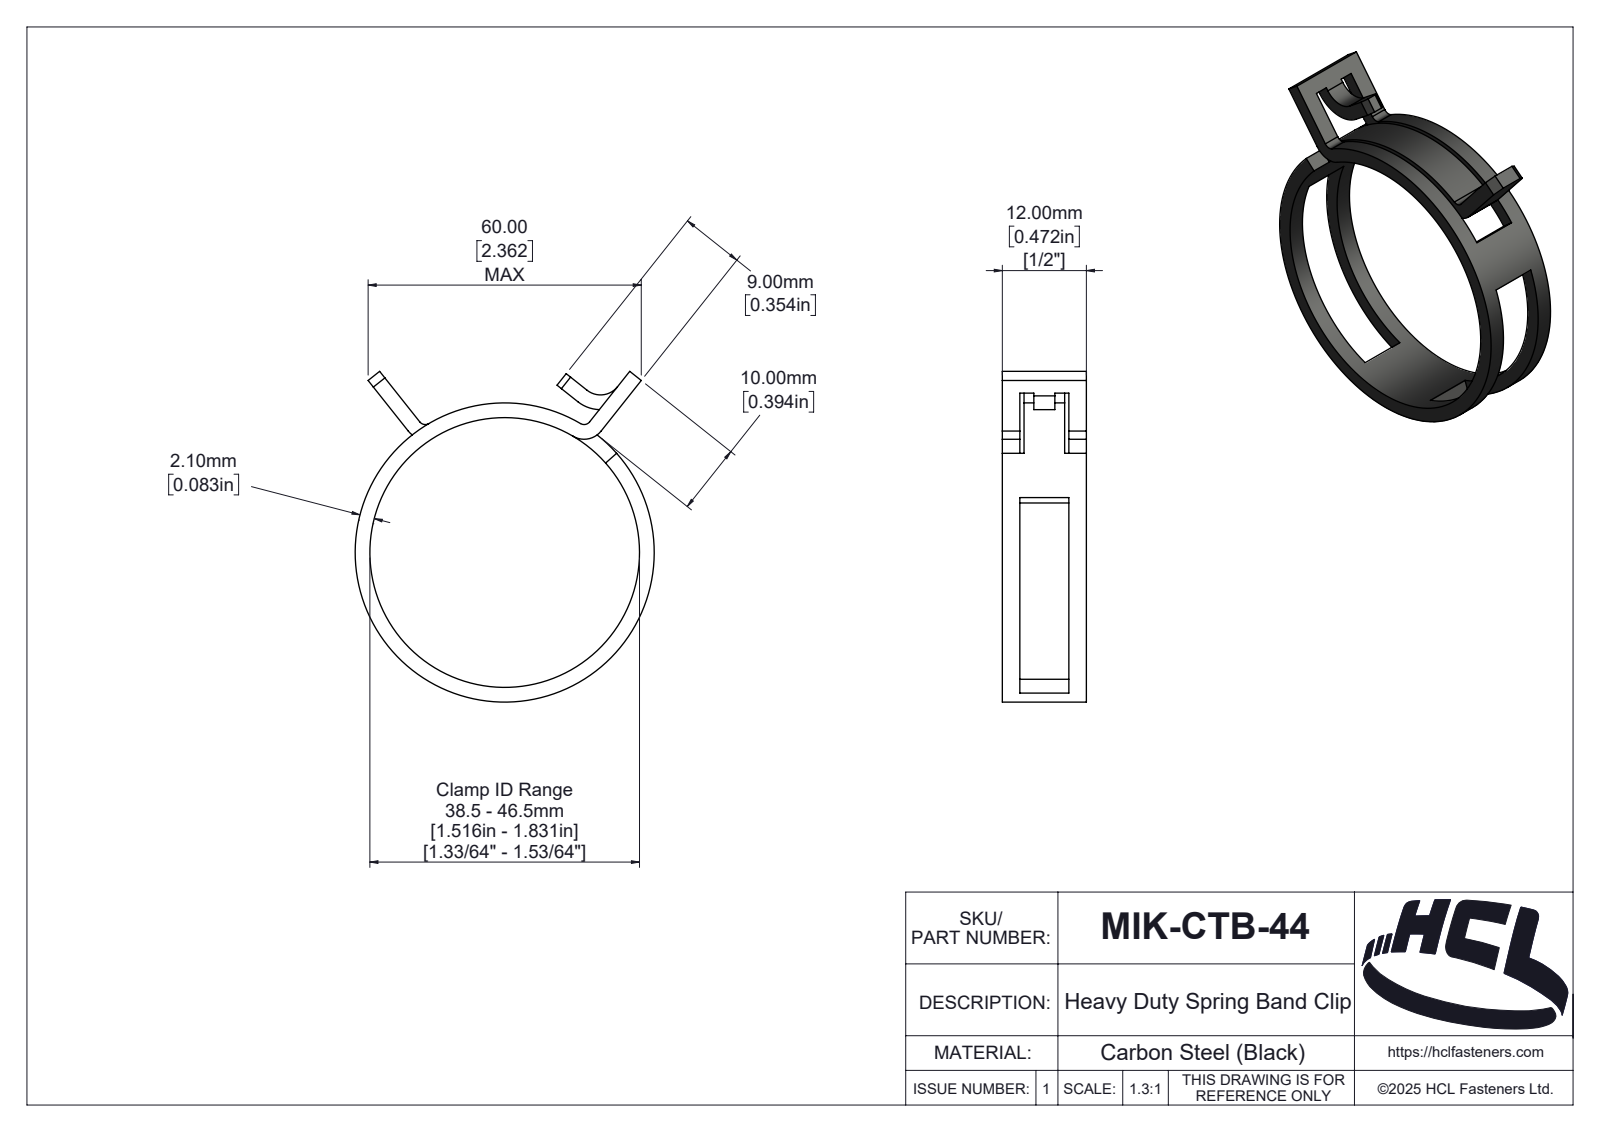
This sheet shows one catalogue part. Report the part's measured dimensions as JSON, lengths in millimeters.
{"part_name": "MIK-CTB-44", "step_written_by": "SolidWorks 2025 (AUTOMOTIVE_DESIGN)", "units": "millimeters", "bodies": {"solids": 1, "faces": 149, "planar": 36, "cylindrical": 64, "other": 49}, "overall_size": [47.2, 42.7, 12], "volume_mm3": 2402, "surface_area_mm2": 3634, "round_holes": [[38.5, 1]], "round_bosses_or_shafts": [[42.7, 1]], "partial_cylinders_radius": [[3.1, 3], [1, 2], [0.33, 1], [1.35, 1], [1.68, 1], [1.77, 1], [2.14, 1], [3.02, 1]], "face_to_face_distances": [2.5, 9.5, 12, 7, 3.1, 8.9, 0.6, 6.4, 2.1, 5.8]}
